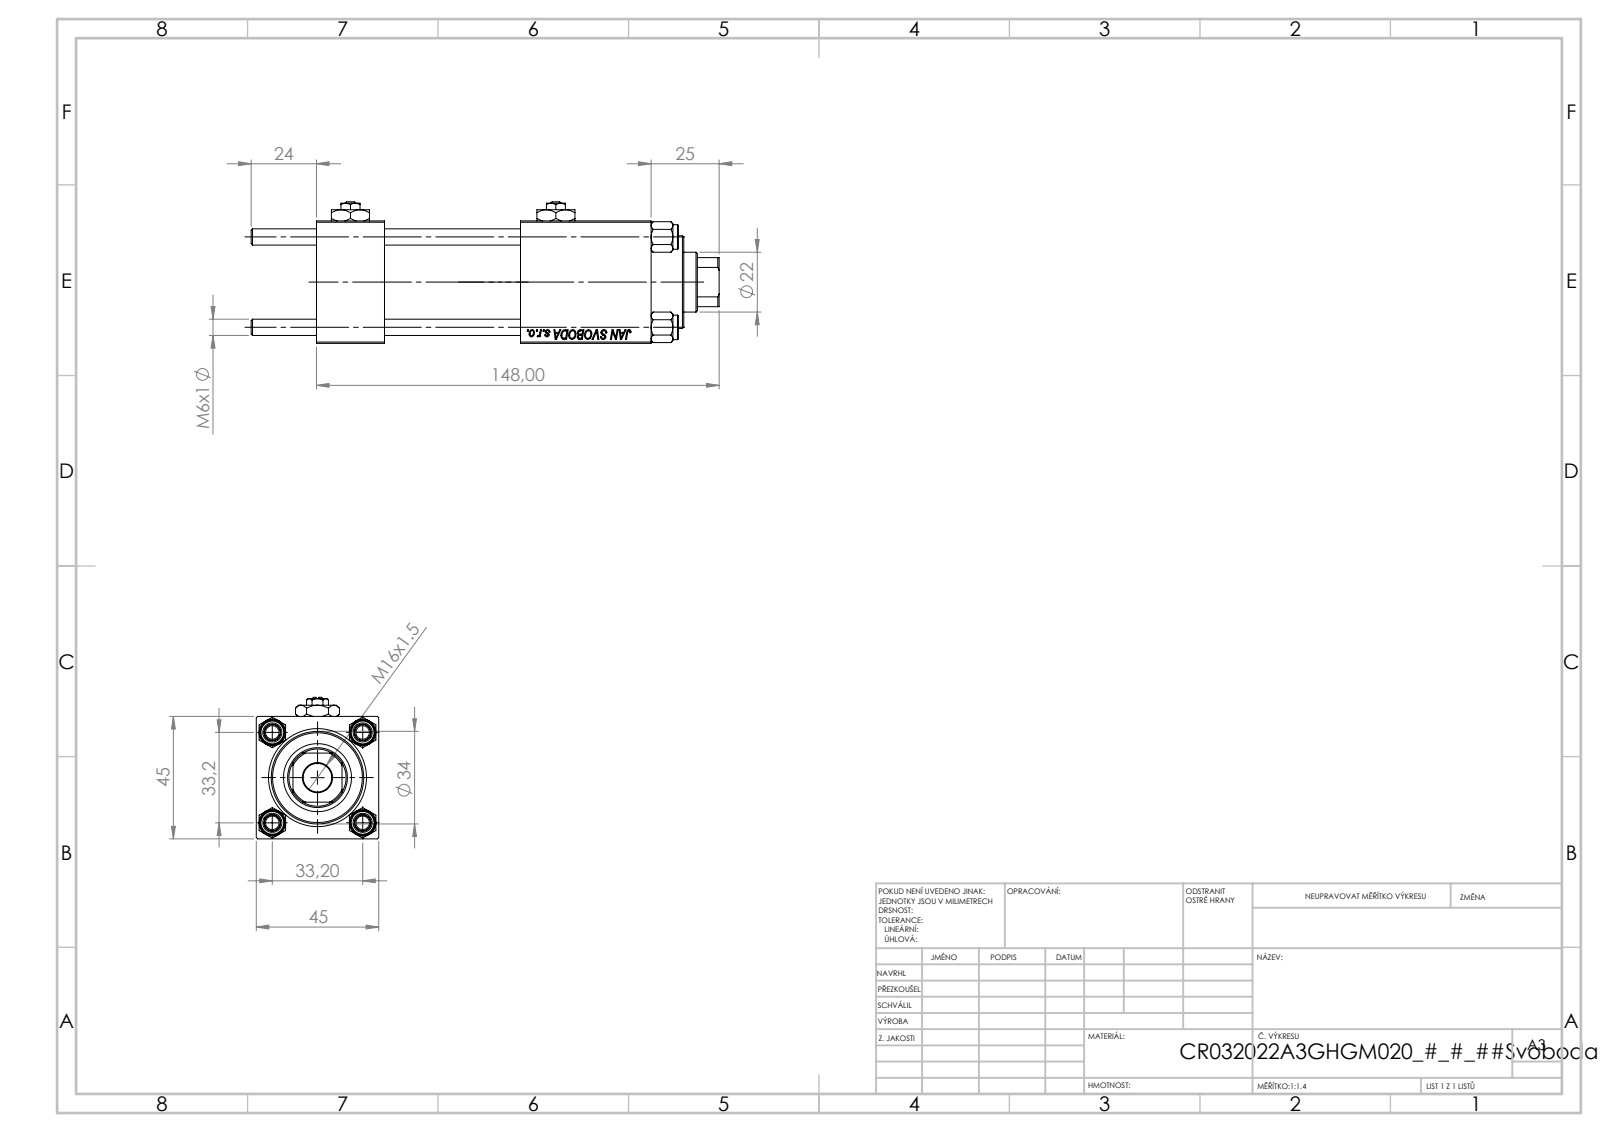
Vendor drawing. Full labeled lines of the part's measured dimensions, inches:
Part name (STEP PRODUCT): CR025_012_A_0_G_A_G_M_020_+#_##_TYCINKA; V215CR_VCP; Zatka_pro_OIL_PORT; NUT_M5 (+2 more)
STEP written by: SolidWorks 2019 (CONFIG_CONTROL_DESIGN)
Units: inches
Bodies: 13 solids, 1232 faces (566 planar, 88 cylindrical, 578 other)
Overall size (bounding box): 6.772 × 2.047 × 1.772
Volume: 12.98 in³ · Surface area: 122.3 in²
Round holes (diameter × count): ⌀0.236 ×4, ⌀0.276 ×2, ⌀0.518 ×2, ⌀0.787 ×2, ⌀0.413 ×1, ⌀0.866 ×1, ⌀0.945 ×1, ⌀0.984 ×1, ⌀1.26 ×1, ⌀1.299 ×1
Round bosses / shafts (diameter × count): ⌀0.354 ×4, ⌀1.496 ×1, ⌀1.339 ×1
Partial cylindrical surfaces — rounded edges, fillets, slot ends (radius × count): R0.413 ×1
Main face-to-face distances: 1.772, 0.984, 4.843, 1.969, 2.953, 3.858, 1.89, 1.764, 3.713, 2.728
Hole centre spacings: 0.924, 1.307, 1.848, 2.972
